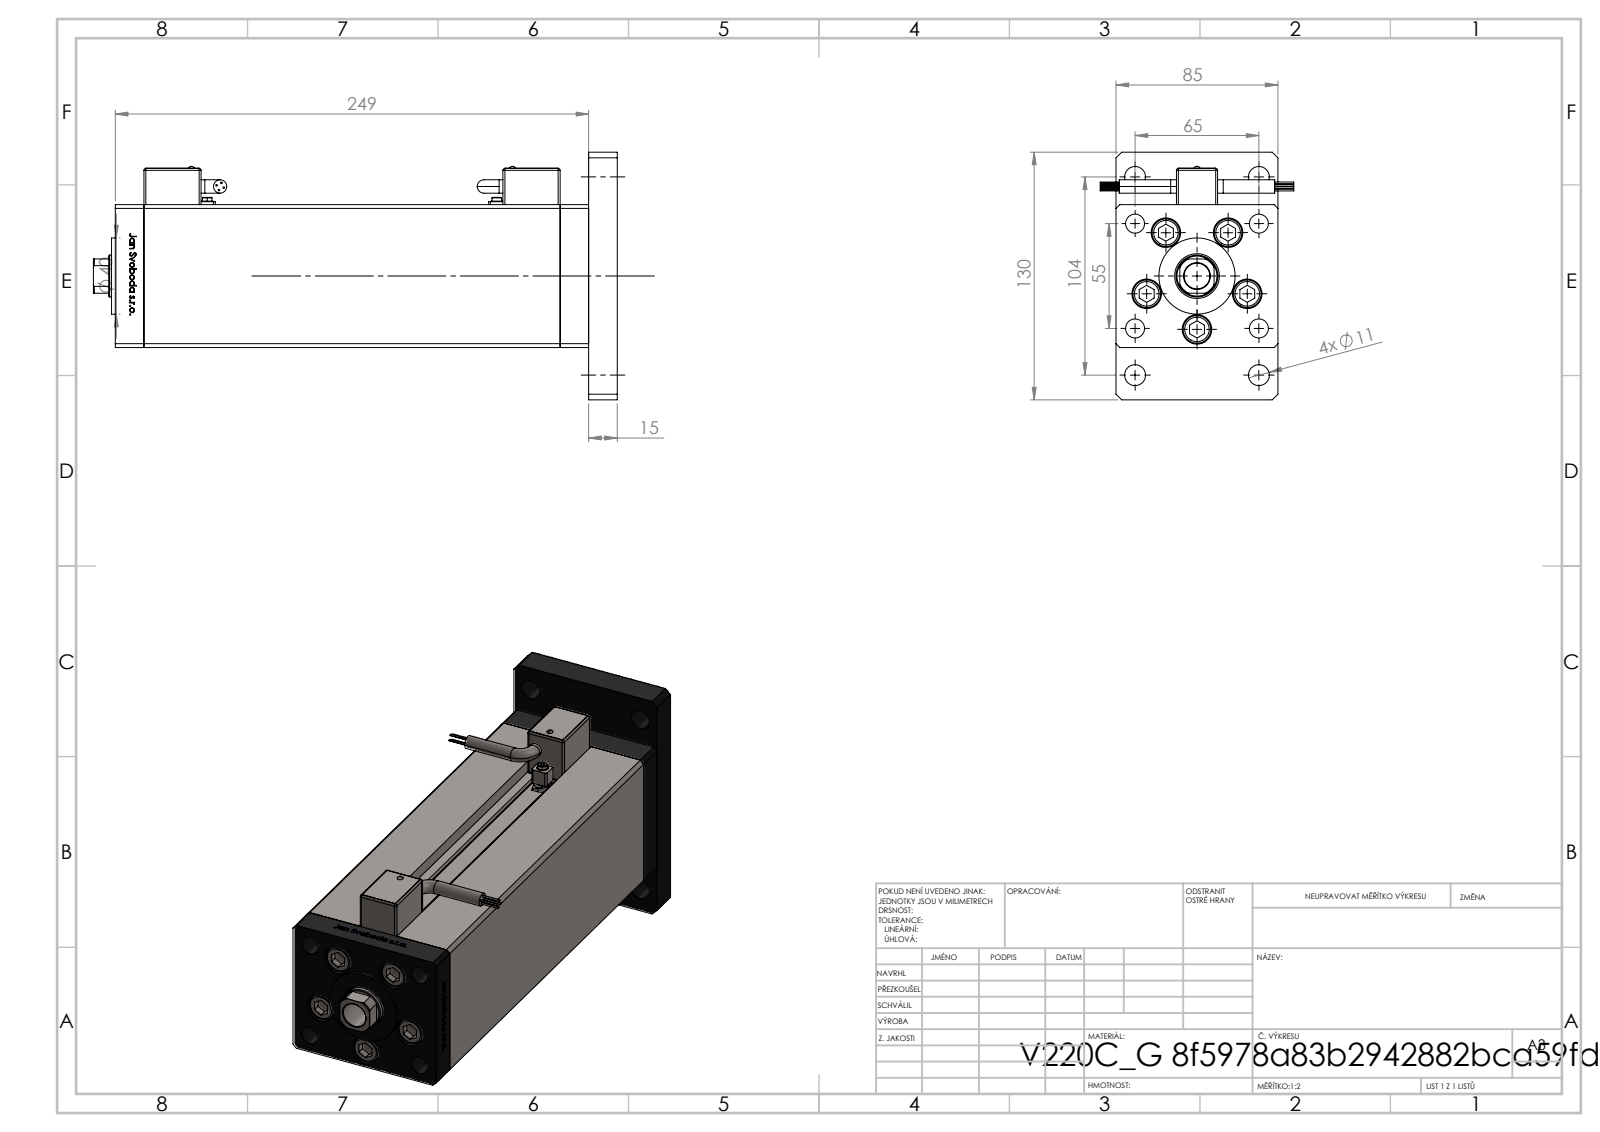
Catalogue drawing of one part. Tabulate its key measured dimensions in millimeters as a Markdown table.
| quantity | value |
| --- | --- |
| part name | V220C_FRONT_G; V220C_G_MIDDLE; V220C BACK_G; V220C_VC_G (+3 more) |
| STEP written by | SolidWorks 2019 (CONFIG_CONTROL_DESIGN) |
| units | millimeters |
| bodies | 21 solids, 1505 faces (592 planar, 271 cylindrical, 642 other) |
| overall size | 275 × 130 × 101.6 |
| volume | 1 570 000 mm³ |
| surface area | 245 032 mm² |
| round holes (diameter × count) | 10 × 9, 11 × 9, 15.5 × 5, 14.5 × 4, 3.6 × 2, 5 × 2, 7 × 2, 13.5 × 1, 22 × 1, 23.5 × 1, 56 × 1 |
| round bosses / shafts (diameter × count) | 8 × 9, 0.85 × 8, 14.5 × 5, 7 × 4, 6 × 2, 3.5 × 2, 2.5 × 2, 40 × 1 |
| partial cylindrical surfaces (radius × count) | 1 × 24, 4 × 4, 0.93 × 2, 10.5 × 1 |
| main face-to-face distances | 15, 85, 75, 233.5, 248.5, 218.5, 30, 2, 246.5, 263.5 |
| hole center spacings | 28, 24.5, 42.57, 61.32, 65, 69.46, 79.5, 102.69 |
